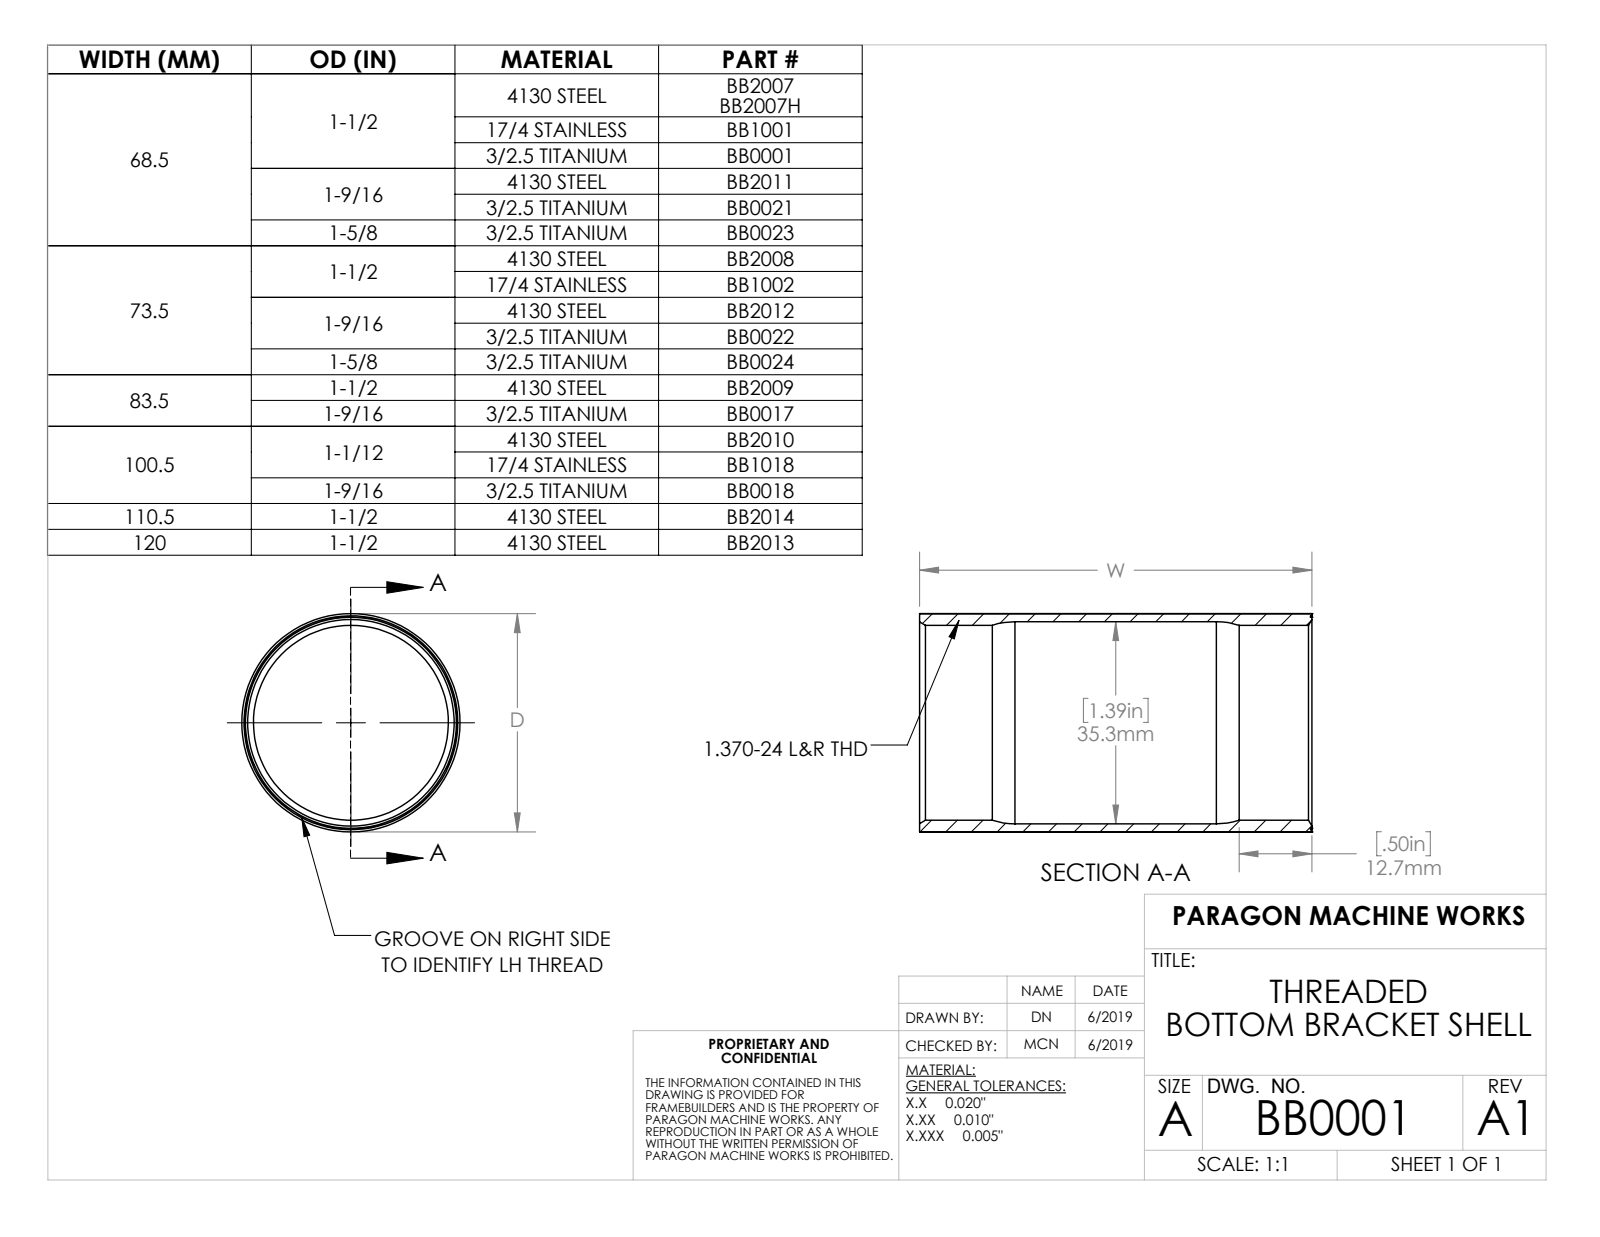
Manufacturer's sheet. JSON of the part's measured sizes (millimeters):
{"part_name": "BB0001", "step_written_by": "SolidWorks 2016 (AUTOMOTIVE_DESIGN)", "units": "millimeters", "bodies": {"solids": 1, "faces": 24, "planar": 4, "cylindrical": 12, "other": 8}, "overall_size": [68.5, 38.1, 38.1], "volume_mm3": 12900, "surface_area_mm2": 16130, "round_holes": [[34, 1], [35.3, 1], [37.3, 1]], "round_bosses_or_shafts": [[38.1, 1], [36.8, 1]], "face_to_face_distances": [68.5, 68.2]}
